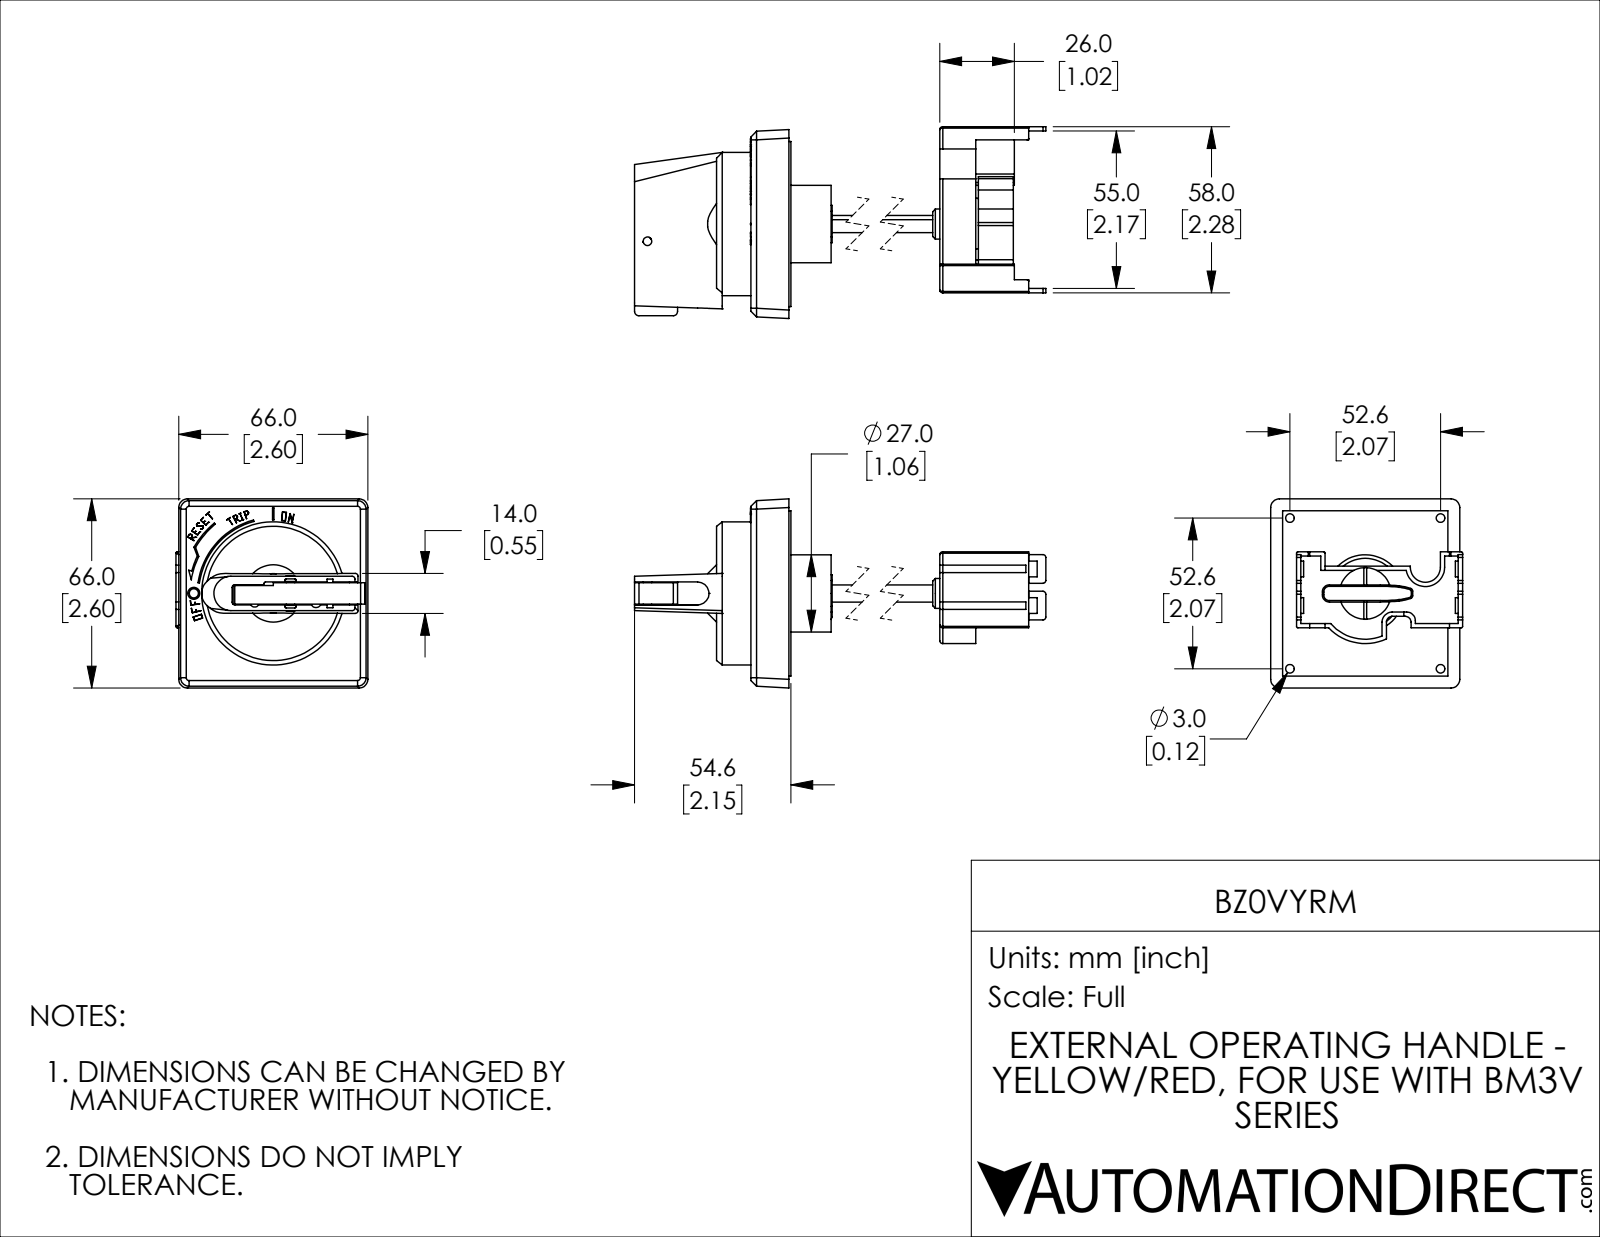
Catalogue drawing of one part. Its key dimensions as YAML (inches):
part_name: "BZ0VYRM"
step_written_by: "SolidWorks 2018 (AUTOMOTIVE_DESIGN)"
units: inches
bodies: {solids: 10, faces: 633, planar: 464, cylindrical: 144, other: 25}
overall_size: [5.699, 2.638, 2.598]
volume: 6.049
surface_area: 75.59
round_holes:
  - {diameter: 0.118, count: 6}
  - {diameter: 0.079, count: 1}
  - {diameter: 0.126, count: 1}
  - {diameter: 0.315, count: 1}
  - {diameter: 0.413, count: 1}
  - {diameter: 0.965, count: 1}
  - {diameter: 1.969, count: 1}
round_bosses_or_shafts:
  - {diameter: 1.063, count: 1}
  - {diameter: 0.709, count: 1}
  - {diameter: 0.453, count: 1}
  - {diameter: 0.165, count: 1}
partial_cylinders:
  - {radius: 0.039, count: 15}
  - {radius: 0.02, count: 14}
  - {radius: 0.079, count: 8}
  - {radius: 0.157, count: 6}
  - {radius: 0.118, count: 5}
  - {radius: 0.016, count: 2}
  - {radius: 0.059, count: 2}
  - {radius: 0.094, count: 2}
face_to_face_distances: [0.059, 0.551, 0.394, 0.157, 0.039, 0.266, 0.256, 0.524, 0.295, 0.236]
hole_center_spacings: [1.464, 2.071, 2.929, 1.035, 1.039, 1.093, 2.343, 2.366]
